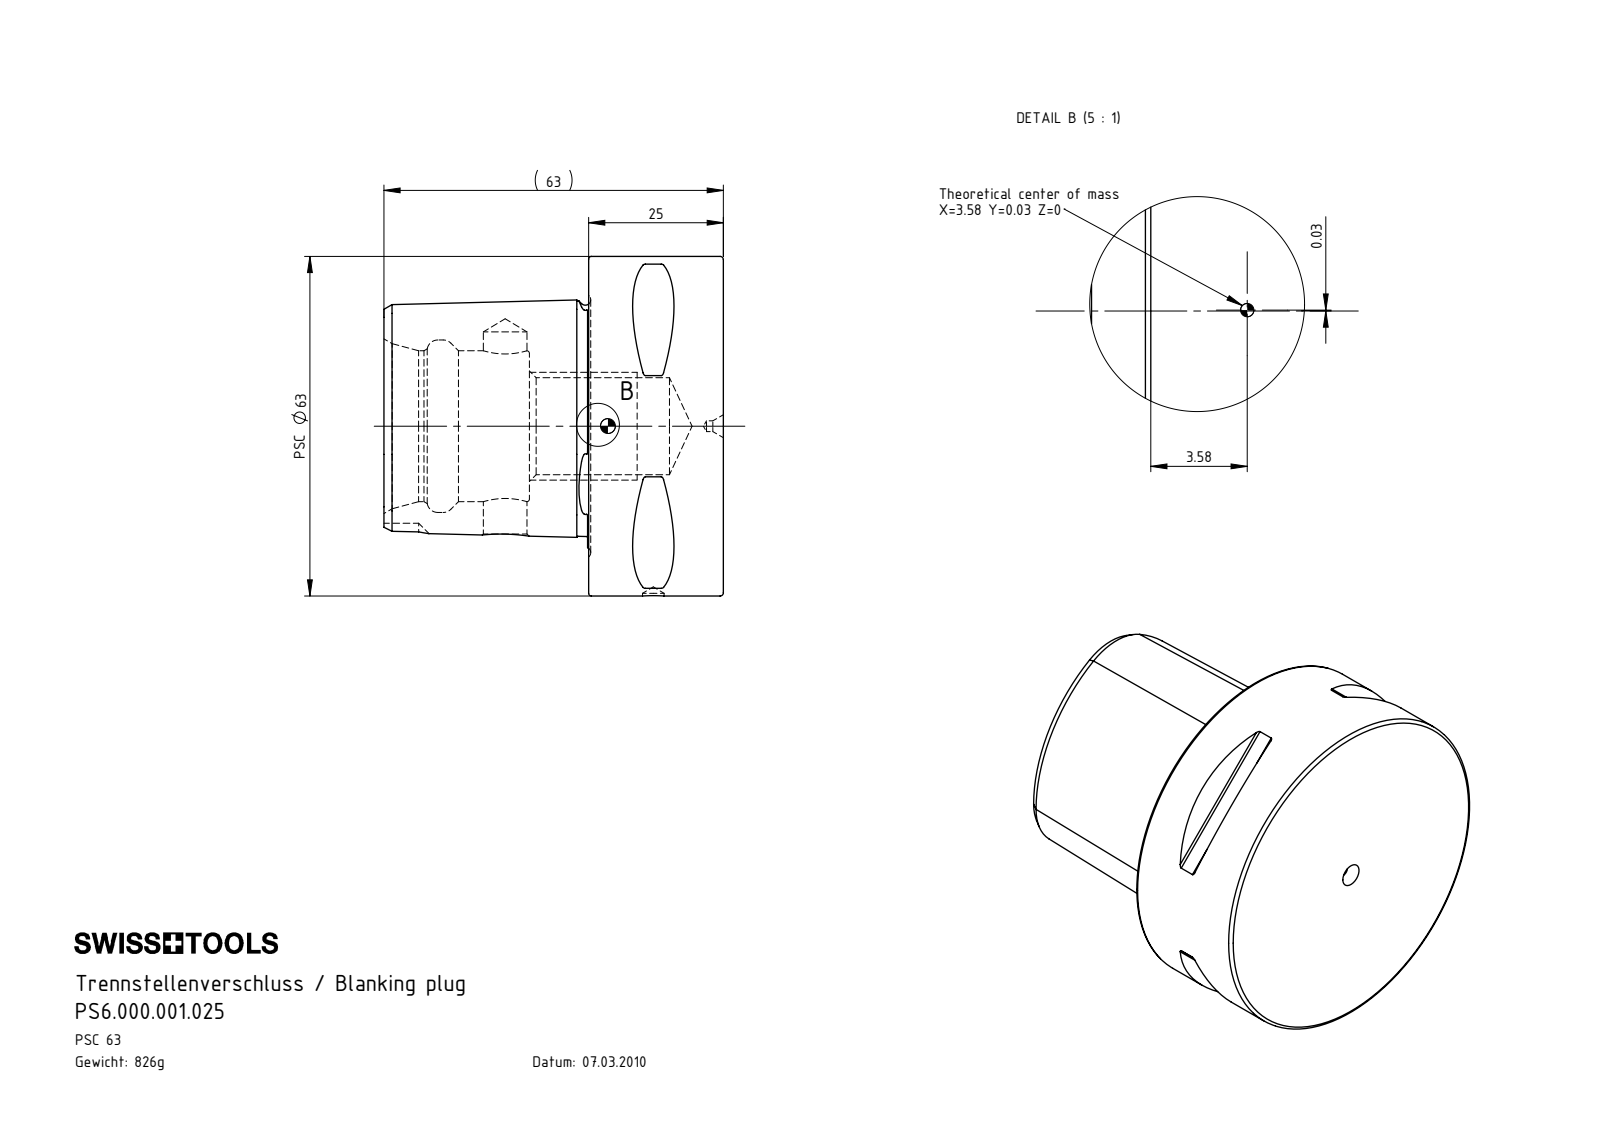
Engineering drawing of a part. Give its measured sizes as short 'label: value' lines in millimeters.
name: PS6.000.001.025
written by: SolidWorks 2017 (AUTOMOTIVE_DESIGN)
unit: mm
bodies: 1 solid, 87 faces (19 planar, 18 cylindrical, 50 other)
size: 63 × 63 × 63
volume: 105 266 mm³; area: 20 495 mm²
holes: 1× ⌀2, 1× ⌀4, 1× ⌀8.1, 1× ⌀18, 1× ⌀28, 1× ⌀32
bosses: 1× ⌀63
rounds: 8× R0.5, 1× R6
face distances: 25, 38, 63, 24.88, 27, 11, 36, 55.8, 37.8, 10.8
hole spacings: 27.5
